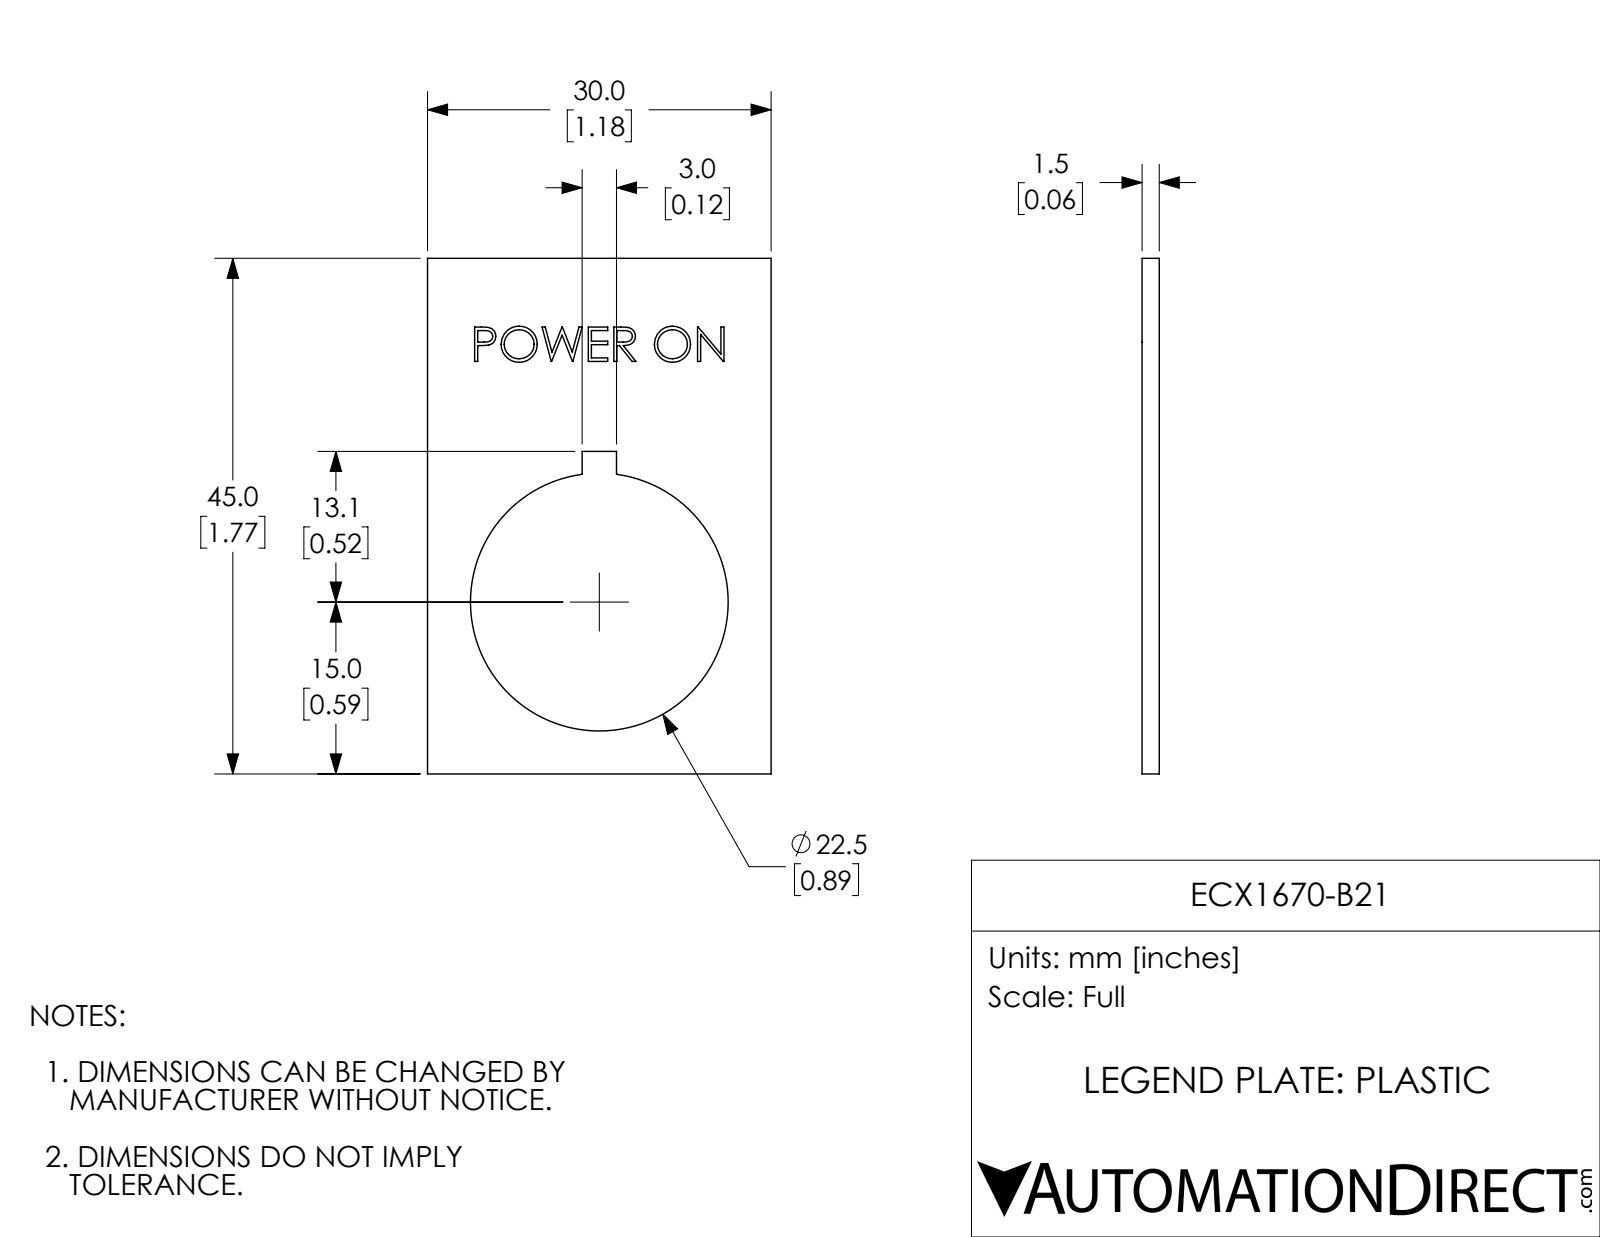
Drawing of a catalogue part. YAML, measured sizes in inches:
part_name: "ECX1670-B21"
step_written_by: "SolidWorks 2017 (AUTOMOTIVE_DESIGN)"
units: inches
bodies: {solids: 1, faces: 104, planar: 74, cylindrical: 3, other: 27}
overall_size: [1.772, 1.181, 0.059]
volume: 0.087
surface_area: 3.462
round_holes:
  - {diameter: 0.886, count: 1}
face_to_face_distances: [0.059, 1.181, 1.772, 0.058, 0.531, 0.65, 1.108, 0.663, 0.118, 0.088]
